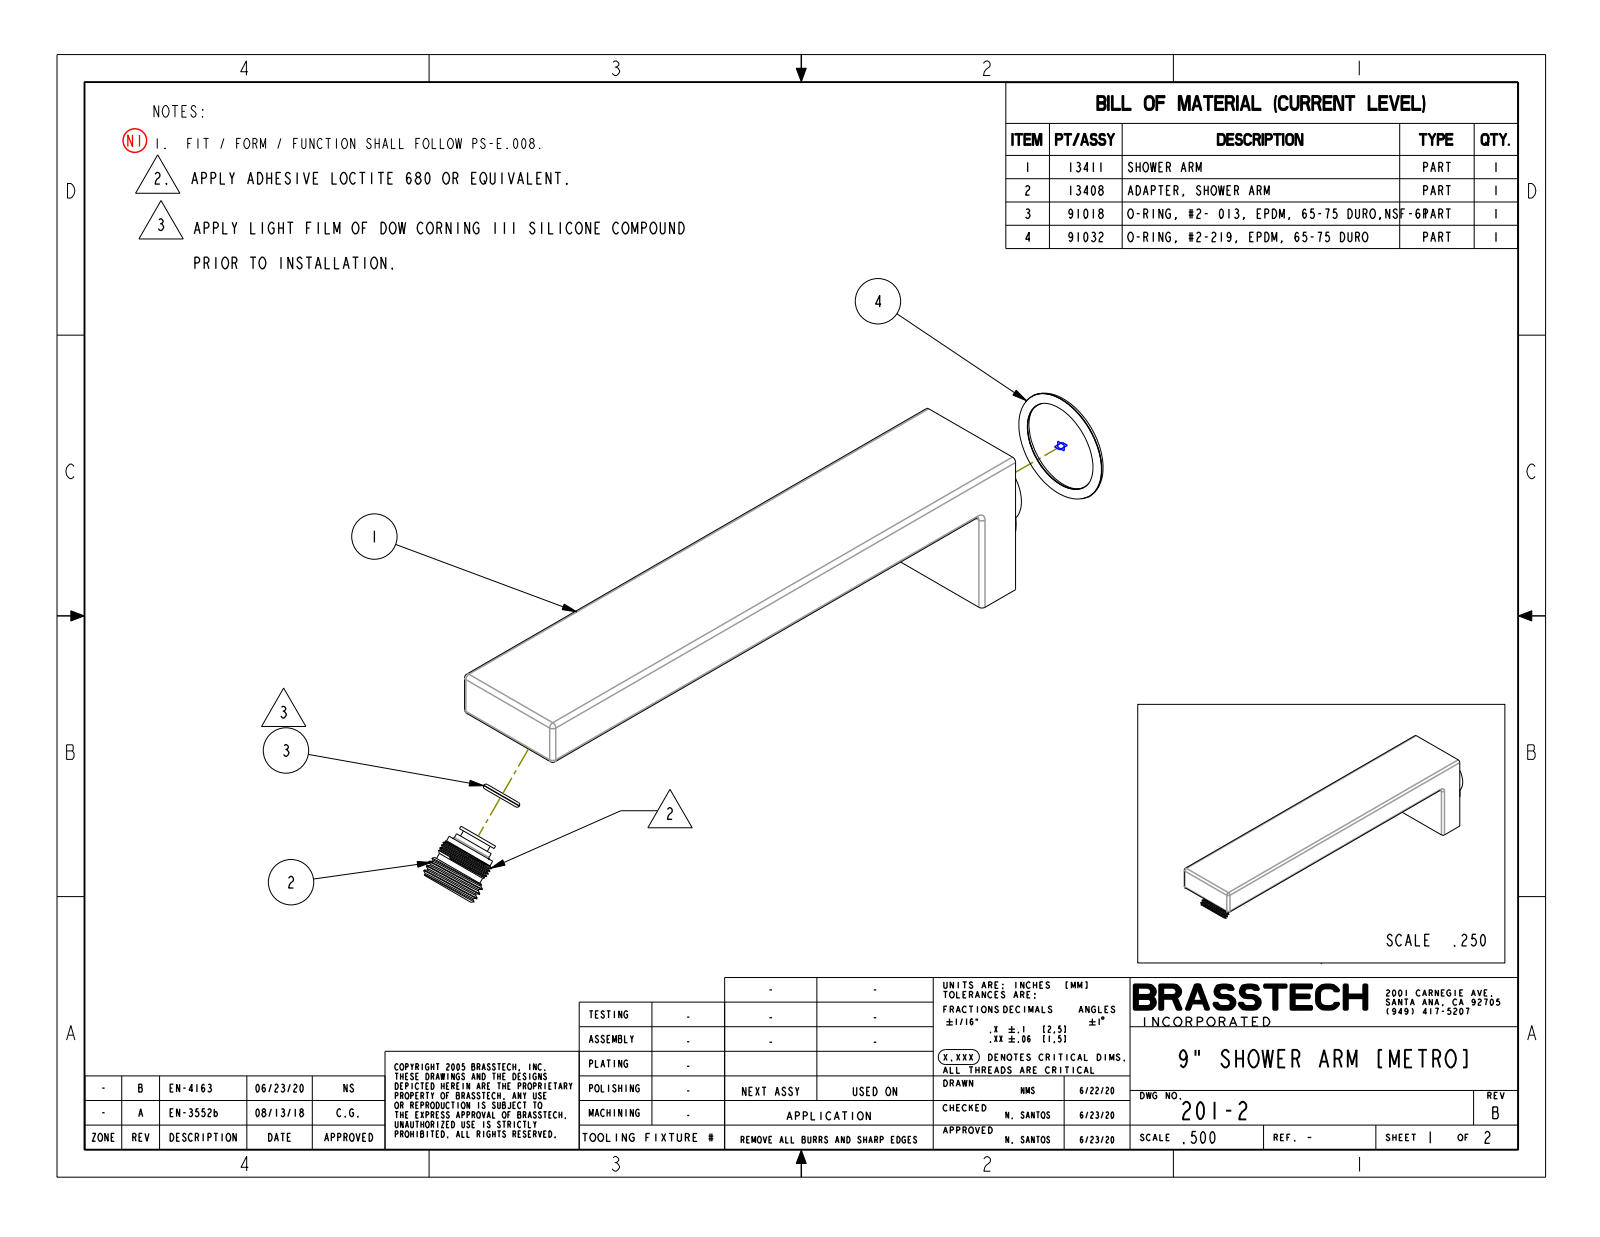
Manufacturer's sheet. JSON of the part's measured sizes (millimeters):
{"part_name": "201-2", "step_written_by": "CREO PARAMETRIC BY PTC INC, 2018400 (AUTOMOTIVE_DESIGN)", "units": "millimeters", "bodies": {"solids": 1, "faces": 118, "planar": 36, "cylindrical": 48, "other": 34}, "overall_size": [239.7, 55.9, 44.5], "volume_mm3": 204200, "surface_area_mm2": 38190, "round_holes": [[14.3, 1], [17.9, 1], [22, 1], [41.9, 1]], "round_bosses_or_shafts": [[44.5, 1], [32.9, 1], [27.9, 1], [20.9, 1], [17.4, 1]], "partial_cylinders_radius": [[1.5, 10], [2, 1], [5.9, 1], [9.7, 1], [11.5, 1], [12.1, 1]], "face_to_face_distances": [16.6, 44.5, 39.3, 55.9, 228.6, 212, 16.9, 228.9, 41.7, 2.4]}
